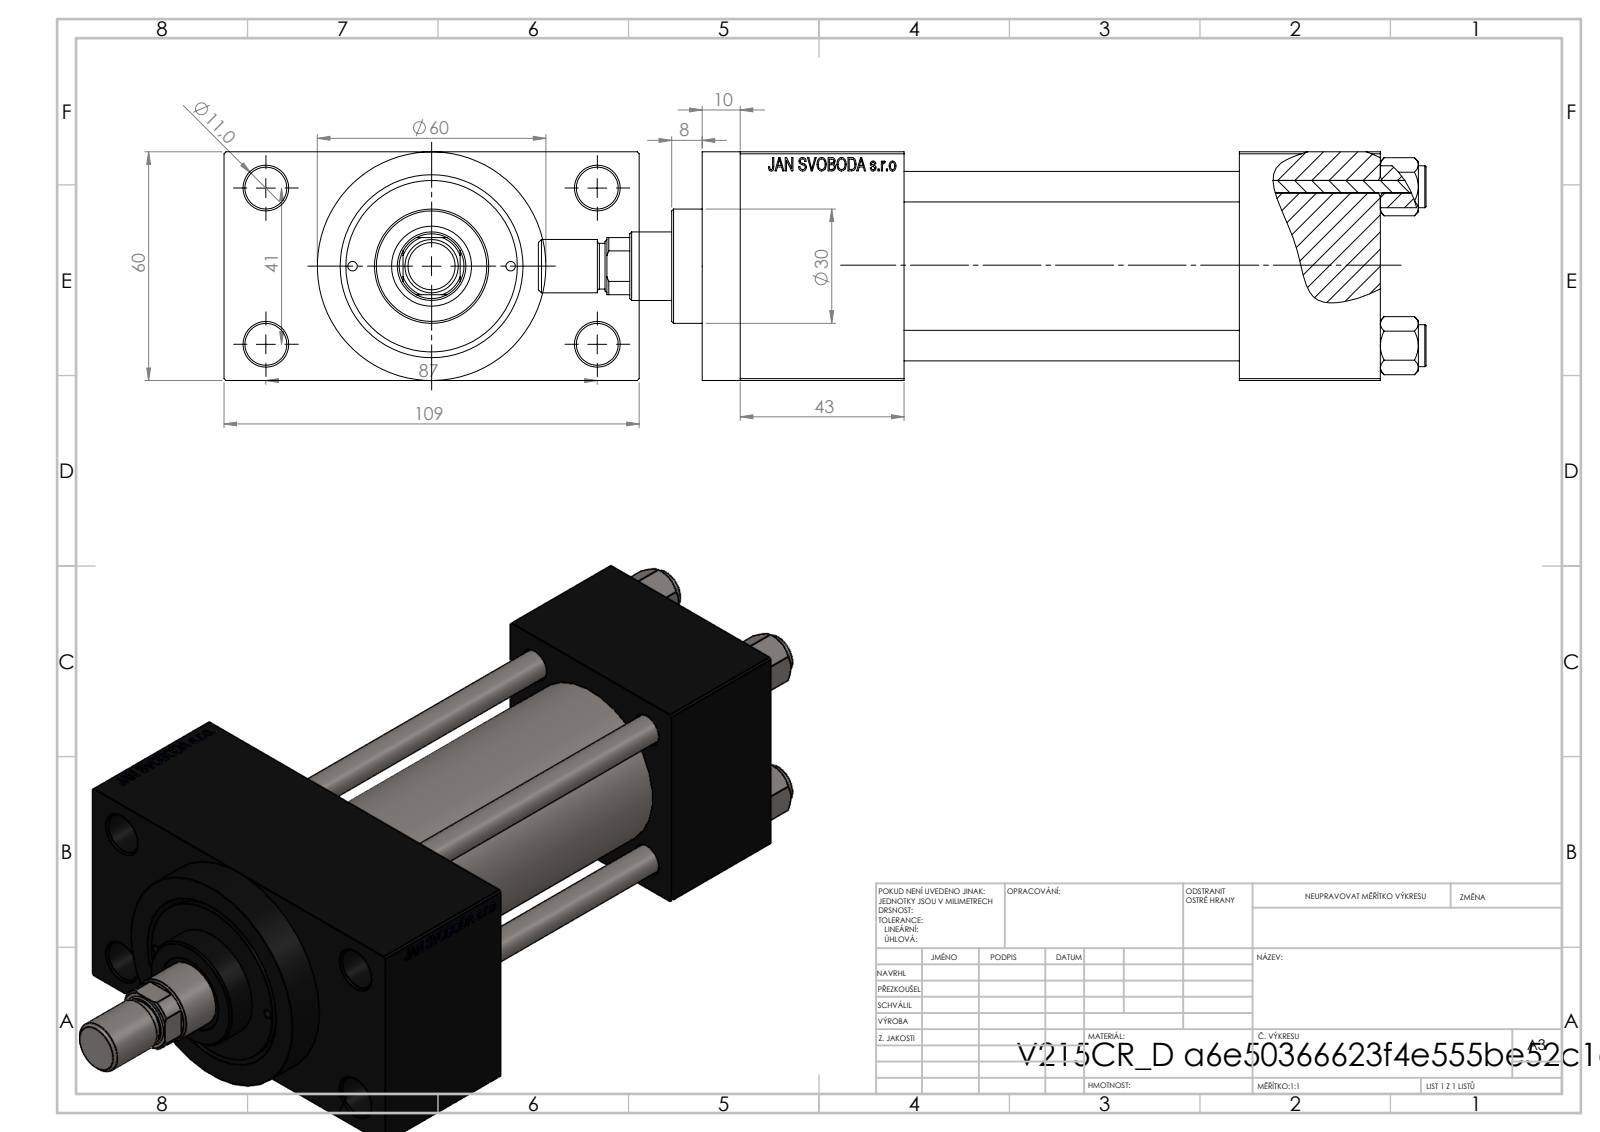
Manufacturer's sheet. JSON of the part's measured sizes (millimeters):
{"part_name": "V215CR_VCP_D; V215CR_D_TYCINKA; NUT_M5_D; V215_VC_A (+2 more)", "step_written_by": "SolidWorks 2019 (CONFIG_CONTROL_DESIGN)", "units": "millimeters", "bodies": {"solids": 12, "faces": 1126, "planar": 504, "cylindrical": 96, "other": 526}, "overall_size": [233, 109, 60], "volume_mm3": 540807, "surface_area_mm2": 136448, "round_holes": [[8, 4], [11, 4], [2.5, 2], [7, 2], [16.66, 2], [24, 2], [8.5, 1], [18, 1], [21, 1], [31, 1], [40, 1], [45, 1]], "round_bosses_or_shafts": [[11, 4], [60, 1], [46, 1], [30, 1], [14, 1], [12, 1]], "partial_cylinders_radius": [[8.5, 1]], "face_to_face_distances": [60, 88, 24.5, 84.5, 37, 125, 43, 168, 131, 134.74], "hole_center_spacings": [20.85, 22.65, 29.49, 30.62, 41.7, 46.53, 47.15, 48.09]}
